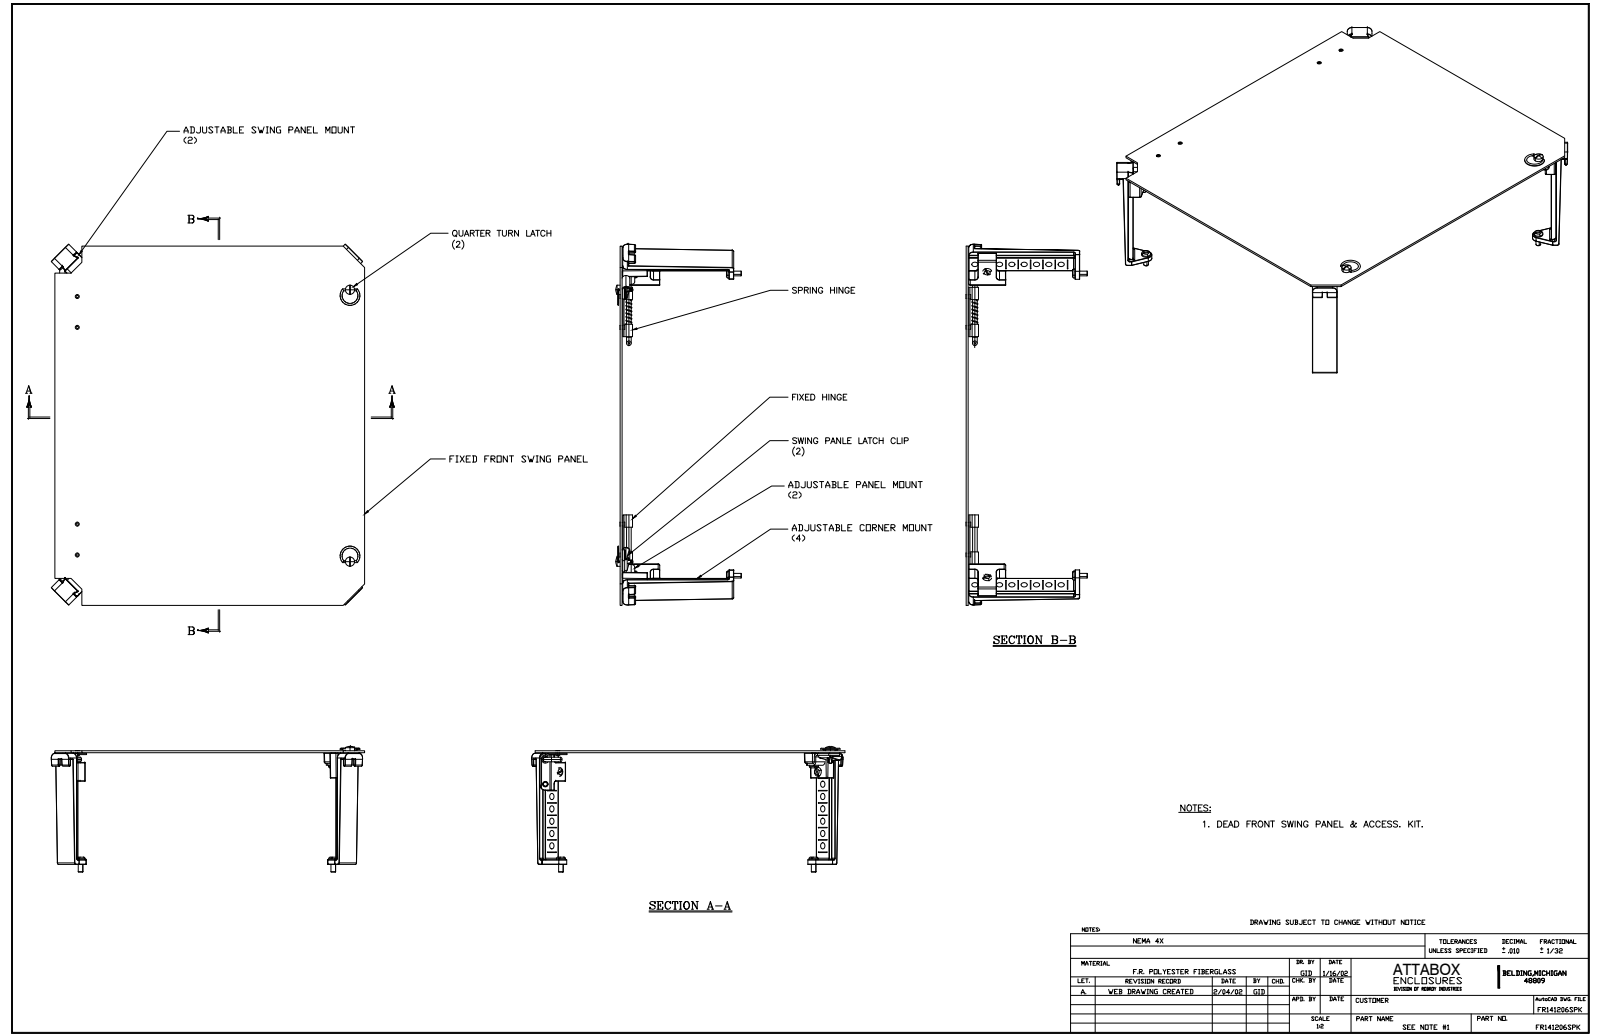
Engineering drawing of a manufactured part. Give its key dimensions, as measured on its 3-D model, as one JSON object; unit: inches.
{"part_name": "FR141206SPK", "step_written_by": "SolidWorks 2019 (AUTOMOTIVE_DESIGN)", "units": "inches", "bodies": {"solids": 48, "faces": 1805, "planar": 834, "cylindrical": 477, "other": 494}, "overall_size": [14.622, 12.716, 5.183], "volume_in3": 23.35, "surface_area_in2": 496.8, "round_holes": [[0.25, 36], [0.156, 6], [0.253, 6], [0.05, 4], [0.14, 4], [0.144, 4], [0.217, 4], [0.22, 4], [0.197, 2], [0.312, 2], [0.35, 2], [0.153, 1]], "round_bosses_or_shafts": [[0.19, 10], [0.373, 6], [0.246, 6], [0.433, 4], [0.315, 4], [0.16, 4], [0.079, 4], [0.394, 2]], "partial_cylinders_radius": [[0.01, 216], [0.06, 44], [0.063, 14], [0.025, 8], [0.13, 6], [0.049, 4], [0.062, 4], [0.19, 4]], "face_to_face_distances": [0.08, 16.953, 0.203, 17.156, 0.167, 0.086, 1, 0.081, 1.413, 7.473], "hole_center_spacings": [0.5, 1.498, 1, 1.731, 1.5, 2.06, 1.413, 2]}
